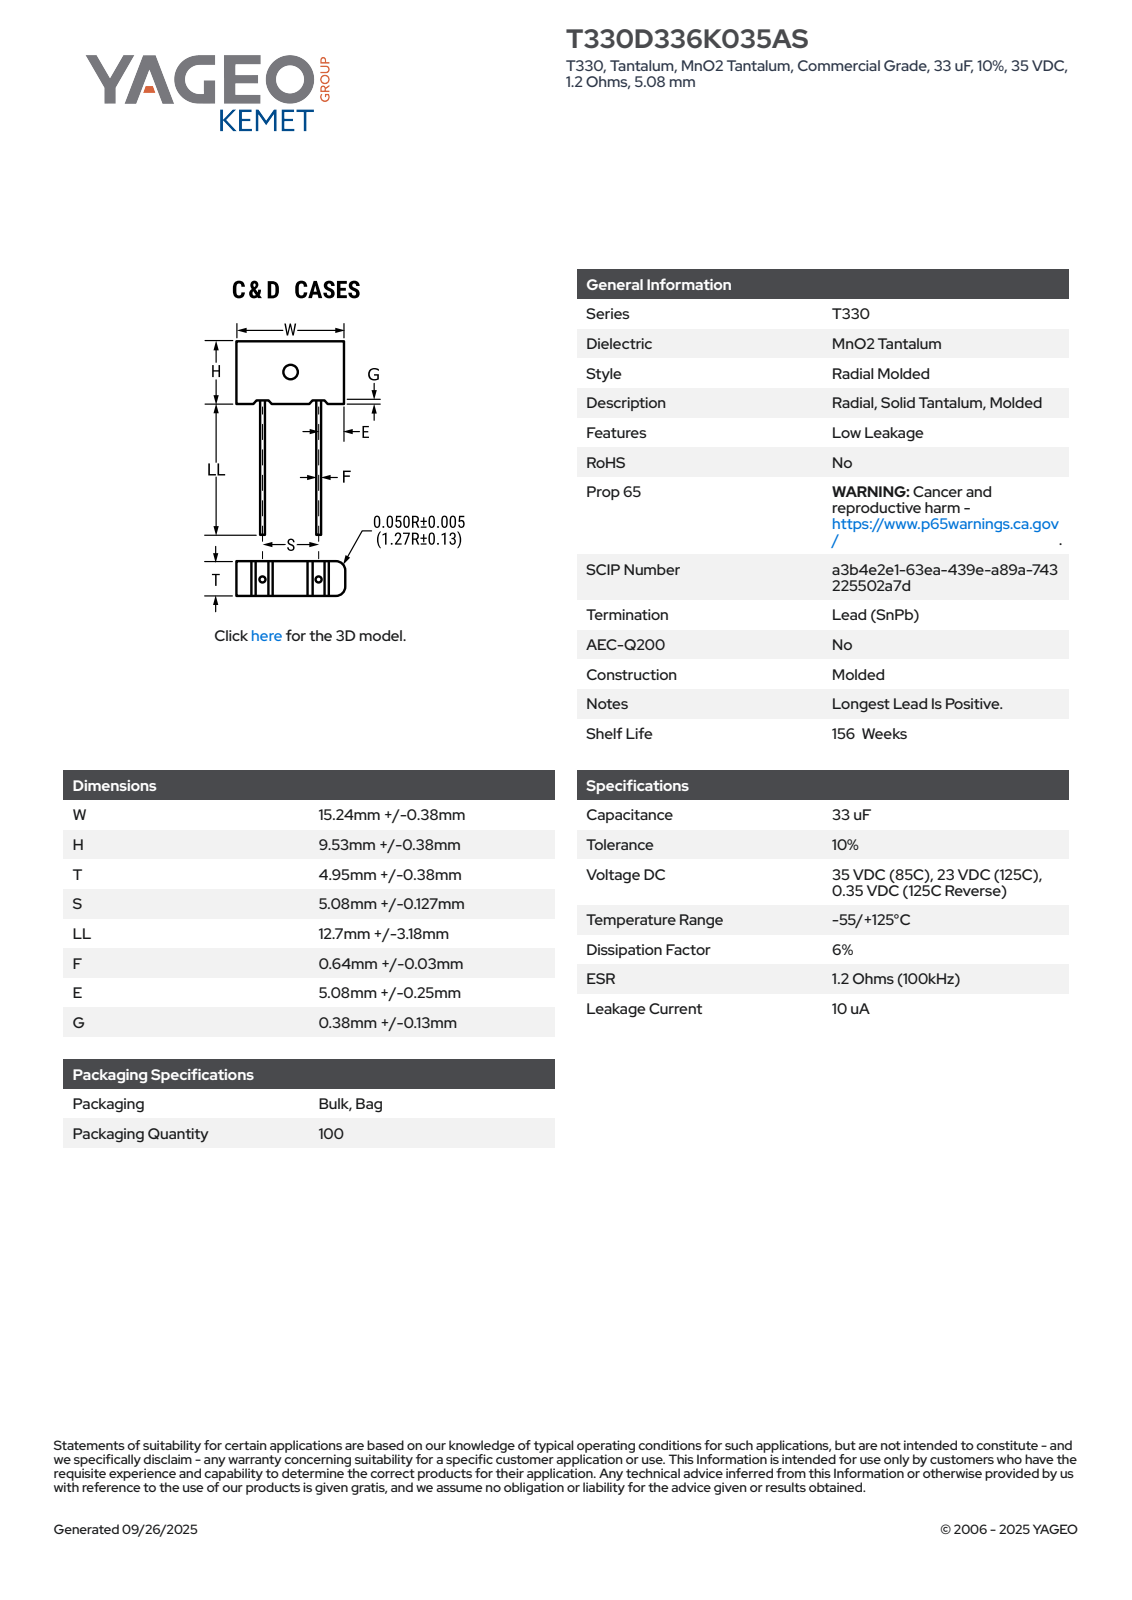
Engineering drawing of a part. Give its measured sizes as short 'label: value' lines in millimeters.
name: CTR_T330CD_W15.62H9.91T5.33S5.08LL15.88F0.67E5.33G0.51
written by: SolidWorks 2014 (AUTOMOTIVE_DESIGN)
unit: mm
bodies: 4 solids, 79 faces (73 planar, 6 cylindrical, 0 other)
size: 25.79 × 15.62 × 4.71
volume: 722 mm³; area: 628 mm²
bosses: 2× ⌀0.67
rounds: 2× R1.4
face distances: 4.7, 9.91, 15.62, 0.51, 9.4, 3.21, 3.37, 4.71, 15.88, 16.39
